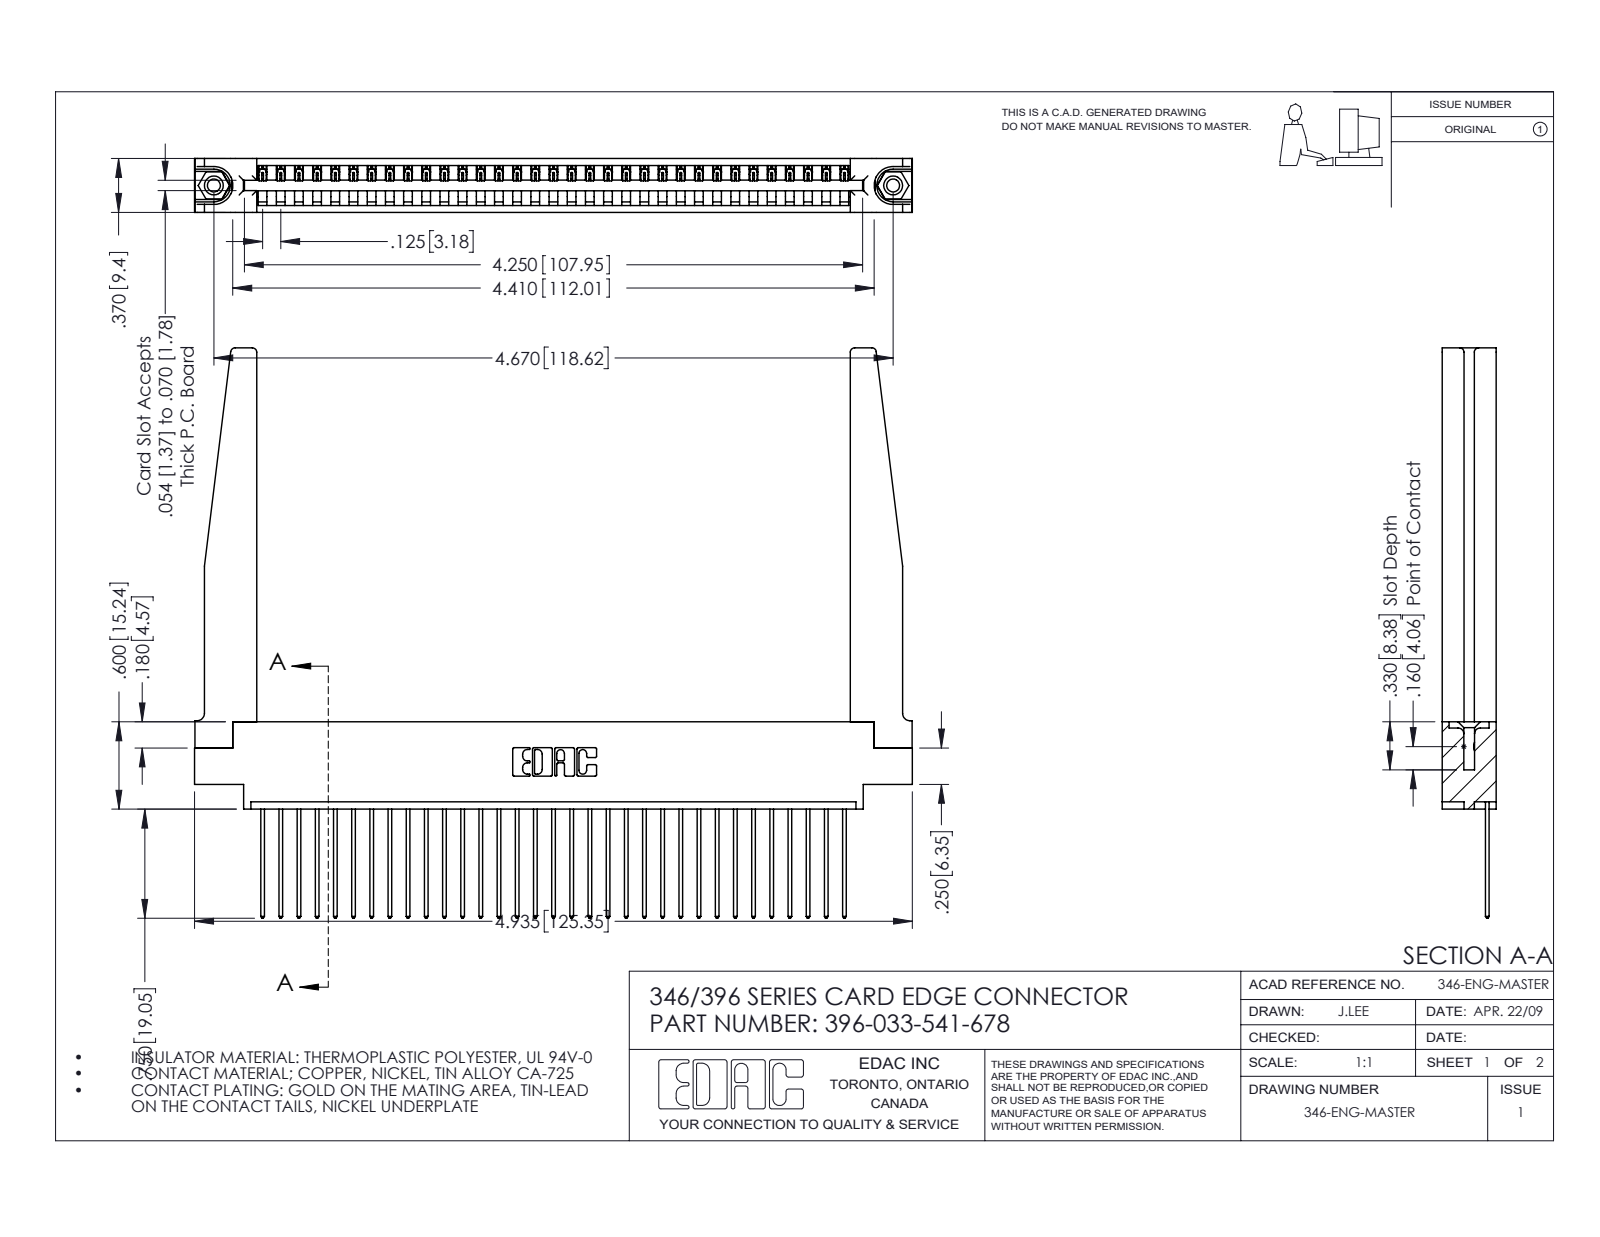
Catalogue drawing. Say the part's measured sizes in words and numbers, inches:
The part is named "396-033-541-678; 345-250-001_345-250-001-102; 346-220-078_345-220-078; 346 Part_0.170 Offset - 0.156 Dia-TH (+1 more)". Its 3-D file was written by "SolidWorks 2016 (CONFIG_CONTROL_DESIGN)". It is 38 solids with 2274 faces: 1542 planar, 680 cylindrical and 52 other. Overall it measures 4.935 by 3.92 by 0.37 inches. Its volume is 1.147 cubic inches and its surface area 34.28 square inches. Round holes: 2 of diameter 0.089, 2 of diameter 0.125, 2 of diameter 0.156, 1 of diameter 0.064. Round bosses or shafts: 2 of diameter 0.155. Partial cylindrical surfaces (rounded edges, fillets, slot ends): 66 of radius 0.006, 66 of radius 0.01, 22 of radius 0.01, 8 of radius 0.03, 6 of radius 0.007, 6 of radius 0.031, 3 of radius 0.026, 2 of radius 0.031. The main face-to-face distances are 0.37, 0.048, 0.322, 0.072, 0.148, 0.15, 0.25, 0.298, 0.025, 0.222. The hole center spacings are 0.246, 4.462, 4.67.
